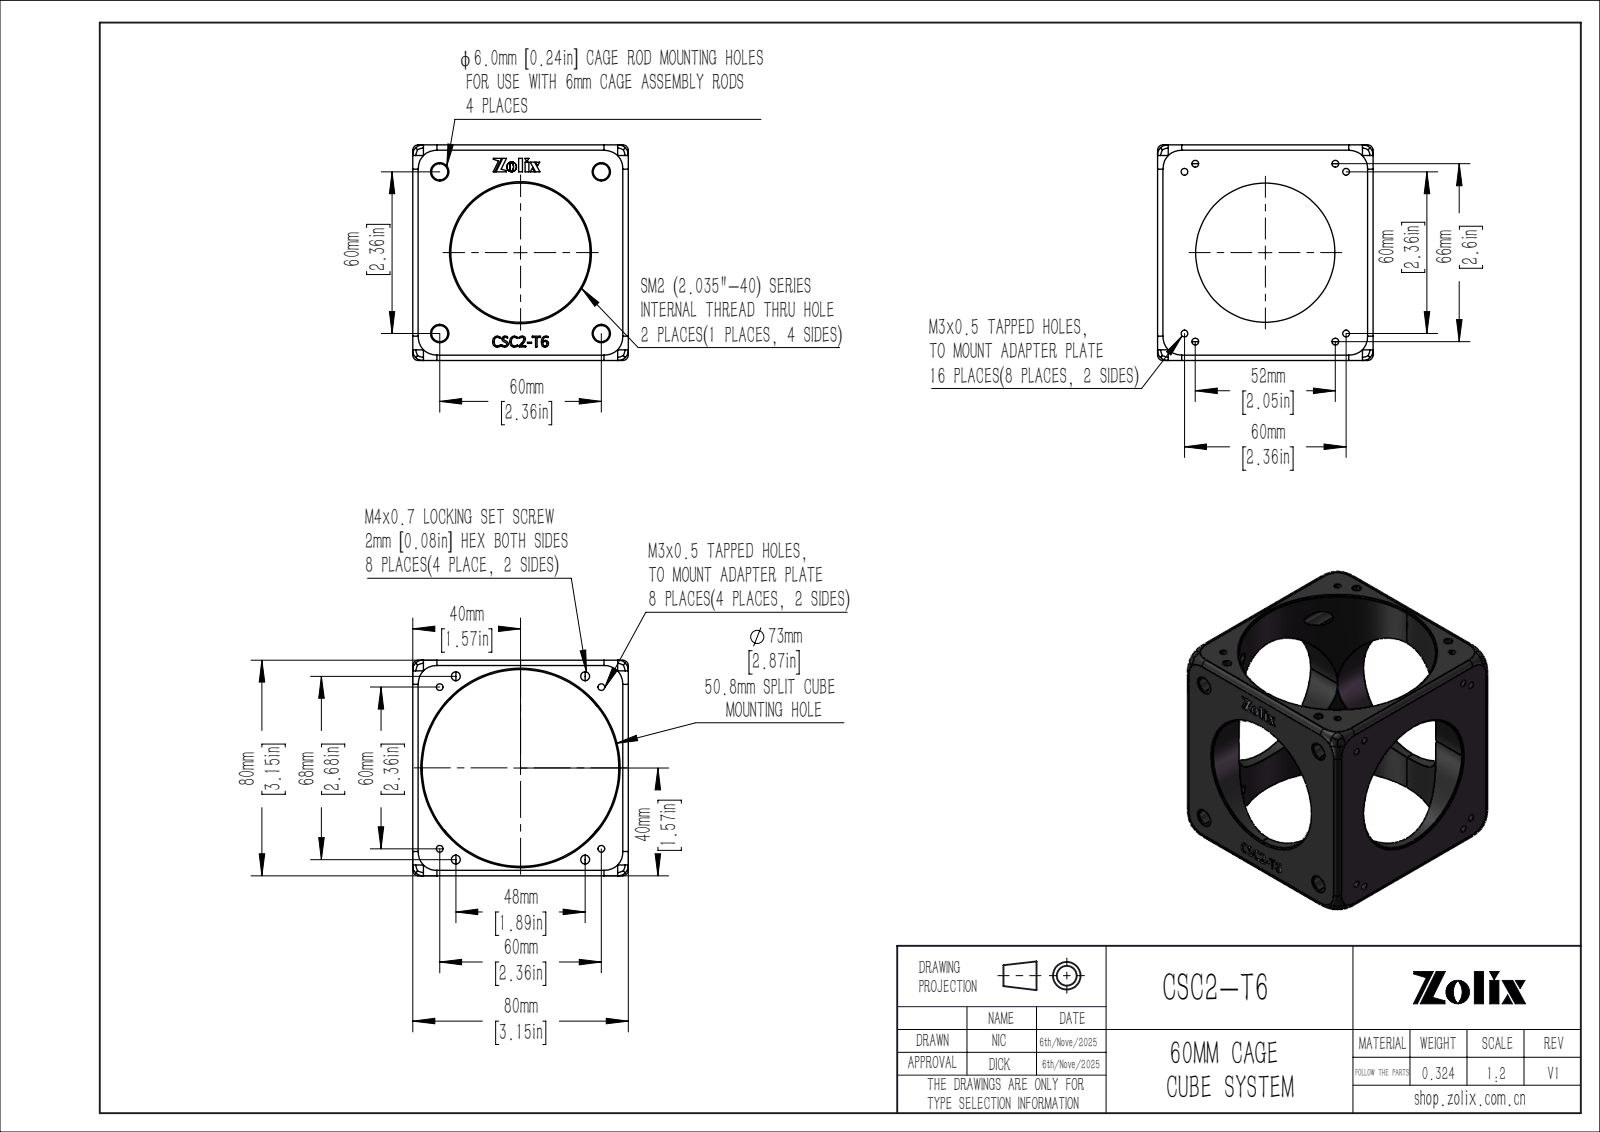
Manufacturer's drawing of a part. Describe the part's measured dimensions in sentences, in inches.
The part is named "CSC2-T6". Its 3-D file was written by "SolidWorks 2020 (CONFIG_CONTROL_DESIGN)". It is 1 solid with 482 faces: 222 planar, 104 cylindrical and 156 other. Overall it measures 3.15 by 3.15 by 3.15 inches. Its volume is 7.313 cubic inches and its surface area 61.55 square inches. Round holes: 12 of diameter 0.098, 4 of diameter 0.13, 4 of diameter 0.236, 2 of diameter 2.035, 1 of diameter 2.874. Partial cylindrical surfaces (rounded edges, fillets, slot ends): 12 of radius 0.079. The main face-to-face distances are 3.15, 0.236, 2.913, 3.149, 2.677, 2.756, 0.157, 0.394, 2.52, 2.362. The hole center spacings are 1.67, 2.362, 3.341, 0.197, 0.284, 1.639, 1.654, 2.132.
